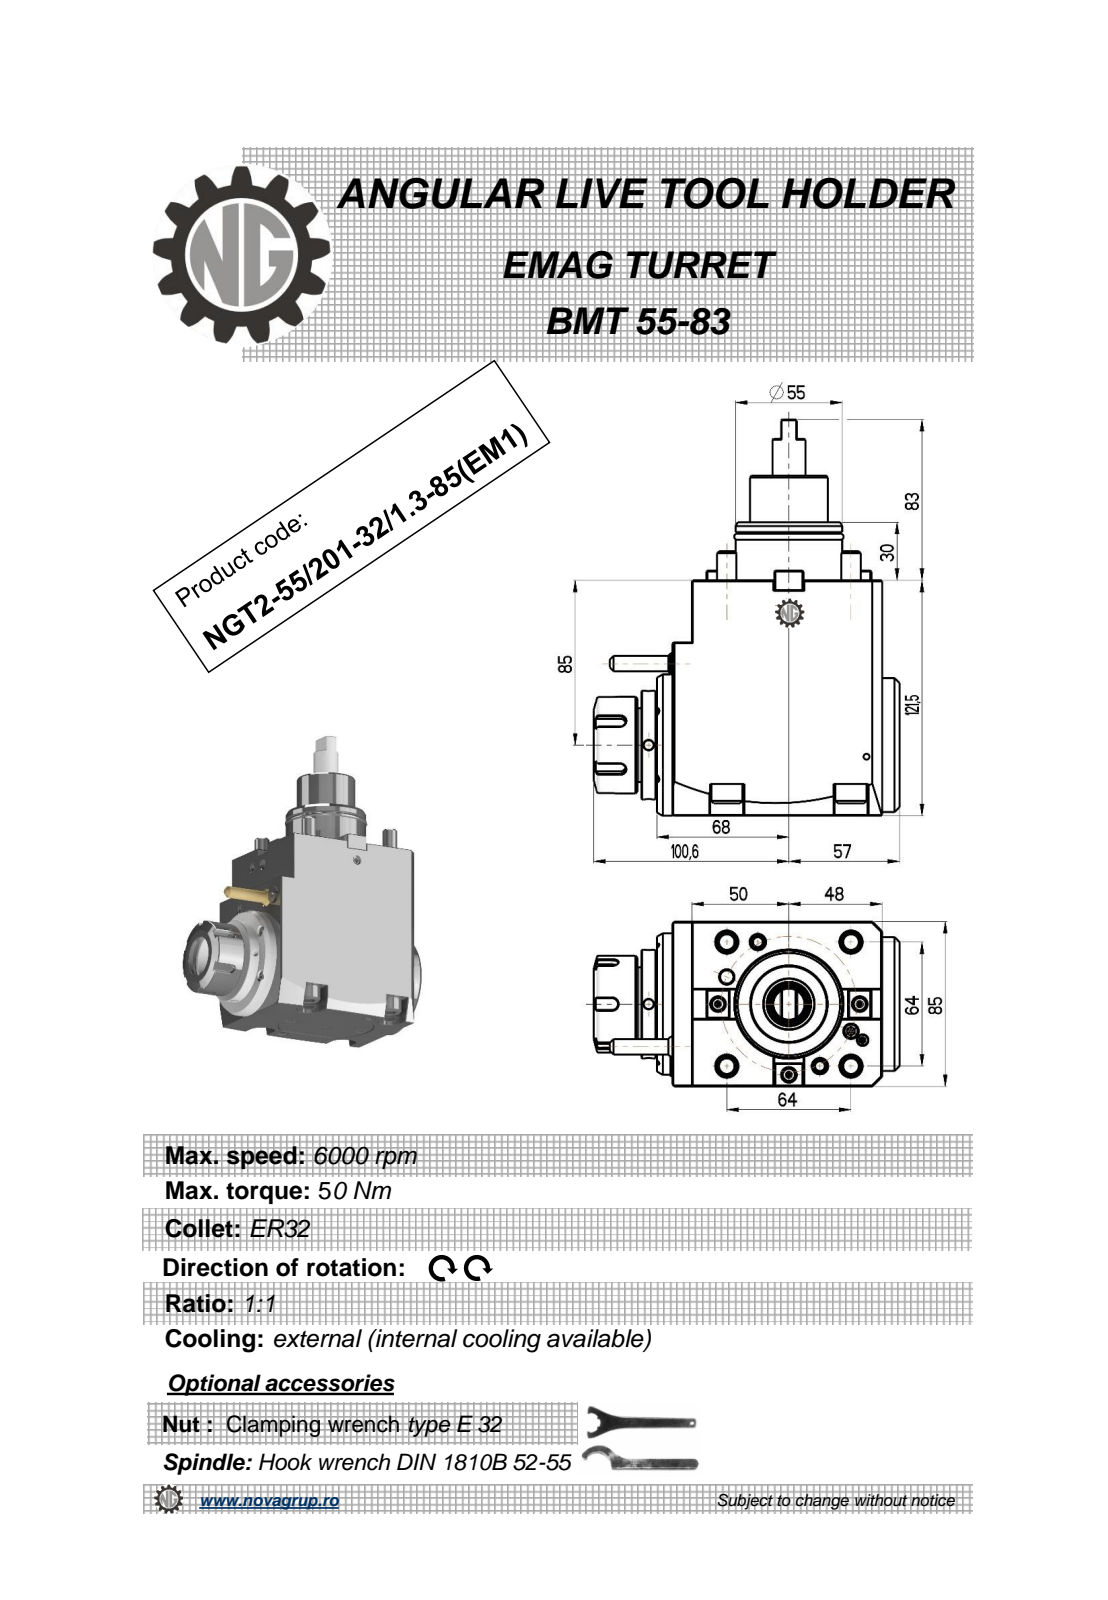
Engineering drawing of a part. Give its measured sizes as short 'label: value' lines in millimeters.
name: NGT2_55_201_32_1_3_85_EM1
written by: PRO/ENGINEER BY PARAMETRIC TECHNOLOGY CORPORATION, 2010280 (CONFIG_CONTROL_DESIGN)
unit: mm
bodies: 2 solids, 472 faces (228 planar, 111 cylindrical, 133 other)
size: 204.5 × 157.6 × 85
volume: 1 298 000 mm³; area: 111 616 mm²
holes: 3× ⌀5, 2× ⌀6.8, 1× ⌀3, 1× ⌀12, 1× ⌀27
bosses: 4× ⌀16, 4× ⌀10, 2× ⌀50, 1× ⌀73, 1× ⌀69, 1× ⌀56, 1× ⌀55, 1× ⌀43.4
rounds: 20× R0.32, 6× R0.22, 5× R3, 4× R8.5, 2× R0.8, 2× R480
face distances: 85, 121.5, 9, 8, 10, 117, 108, 107, 18, 98
hole spacings: 42.62, 47.41, 69.86, 105.19
